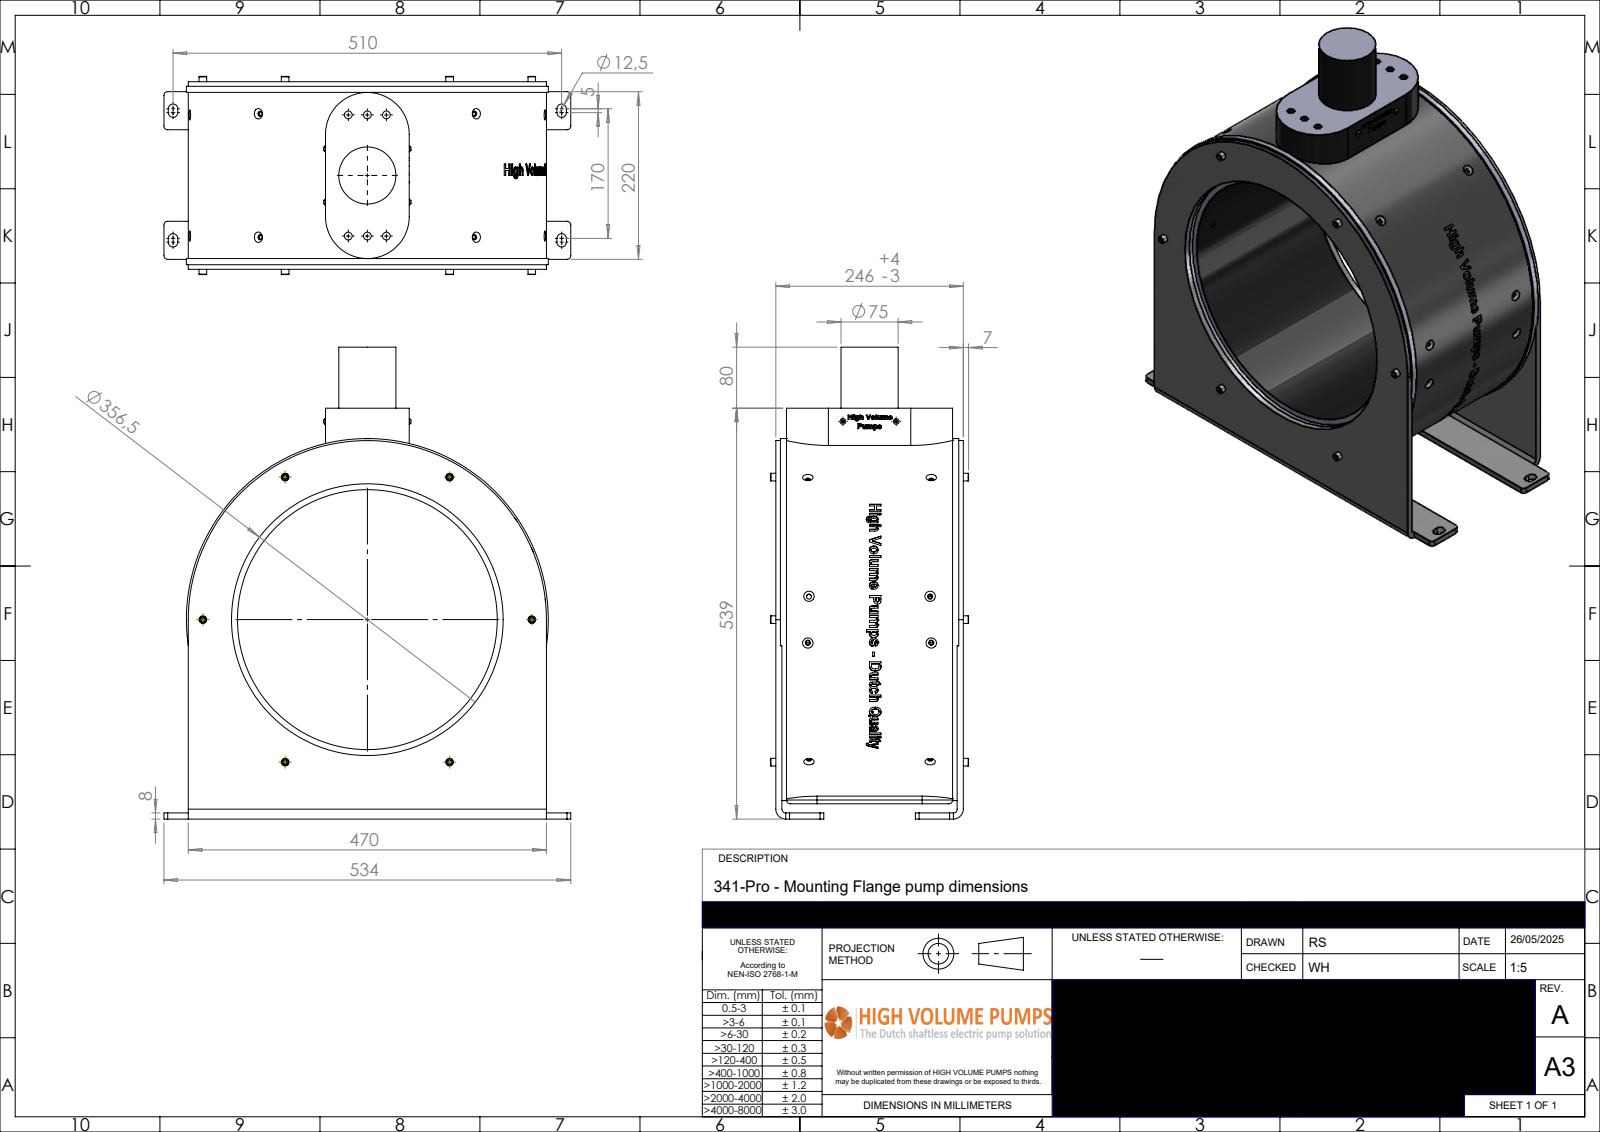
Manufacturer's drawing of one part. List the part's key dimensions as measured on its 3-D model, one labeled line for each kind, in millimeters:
Part name (STEP PRODUCT): P-341-530-rev-A-MF
STEP written by: SolidWorks 2024 (AUTOMOTIVE_DESIGN)
Units: millimetres
Bodies: 1 solid, 1451 faces (773 planar, 175 cylindrical, 503 other)
Overall size (bounding box): 619.07 × 534 × 260
Volume: 22 440 000 mm³ · Surface area: 1 131 000 mm²
Round holes (diameter × count): ⌀6.6 ×22, ⌀5 ×16, ⌀6.7 ×6, ⌀10.2 ×6, ⌀341 ×1, ⌀356.5 ×1, ⌀357 ×1
Round bosses / shafts (diameter × count): ⌀11.57 ×6, ⌀10 ×6, ⌀6 ×6, ⌀7.6 ×2, ⌀475 ×1, ⌀470 ×1, ⌀75 ×1
Partial cylindrical surfaces — rounded edges, fillets, slot ends (radius × count): R5 ×15, R6.25 ×8, R13 ×2, R40 ×2, R55 ×2, R234.5 ×1, R237.6 ×1
Main face-to-face distances: 8, 246, 238, 6, 232, 230, 14, 224, 539.07, 531.07
Hole centre spacings: 215.85, 160.5, 159, 1.52, 1.56, 25, 160.95, 162
